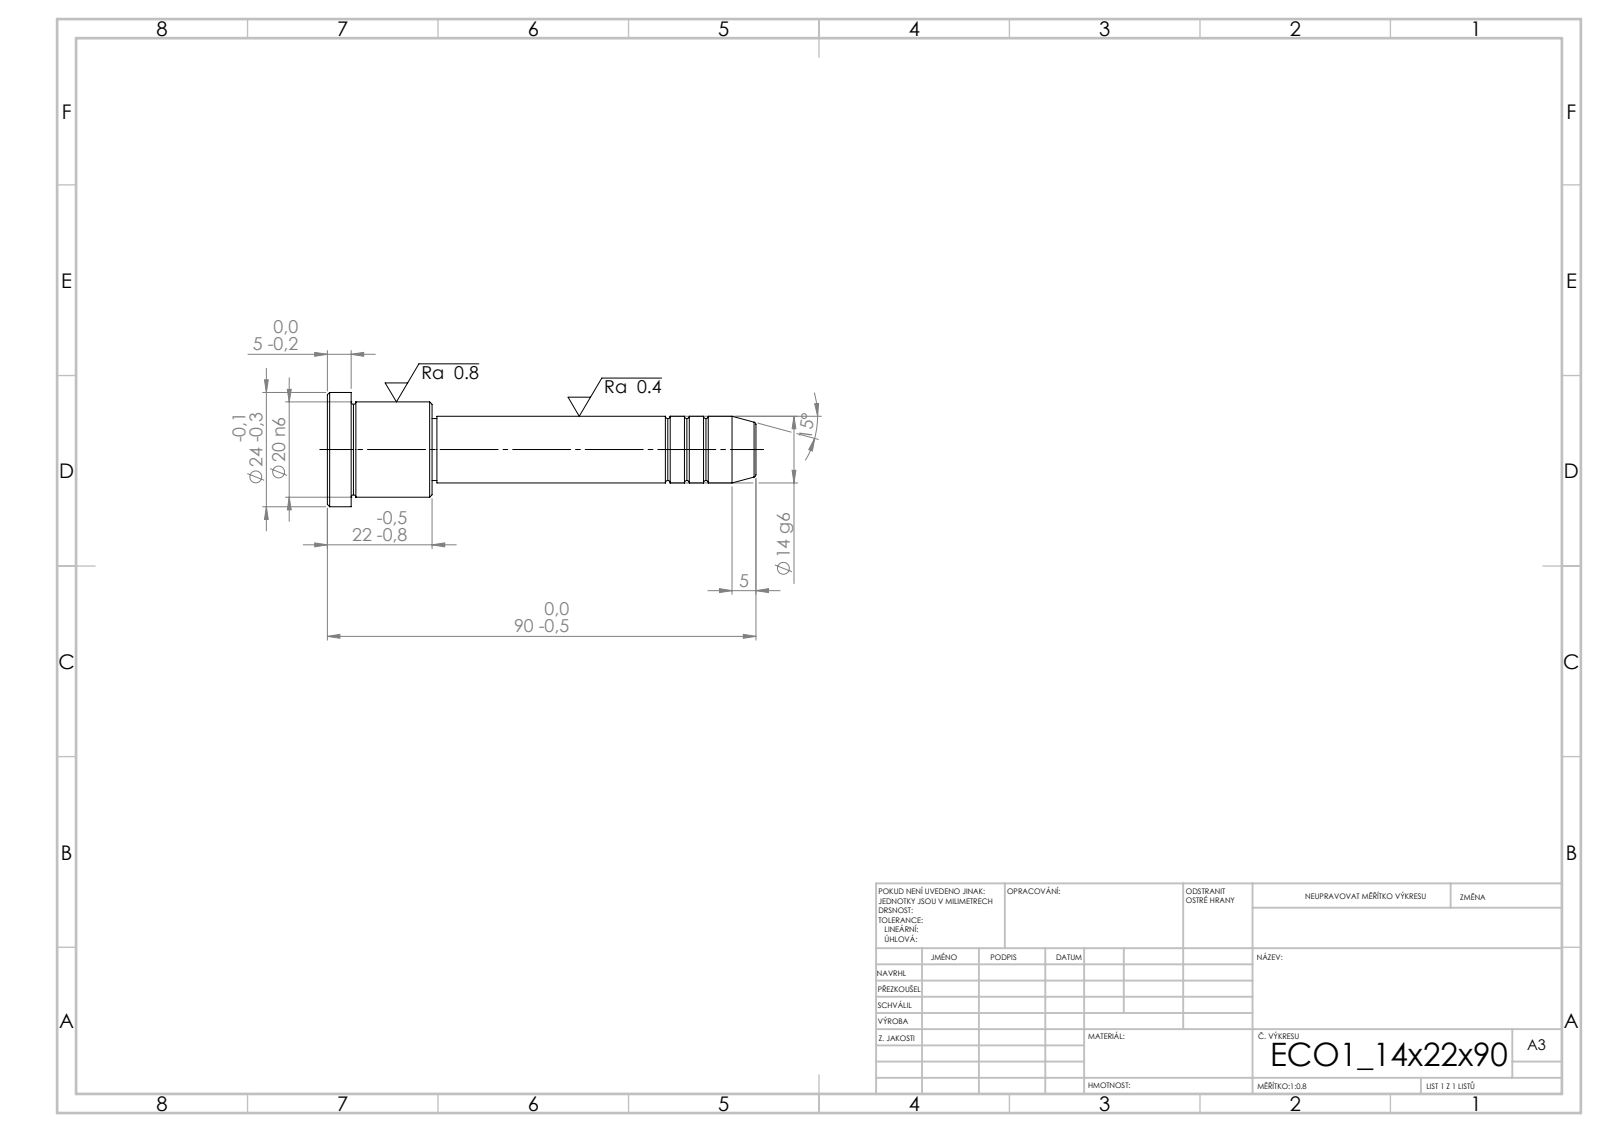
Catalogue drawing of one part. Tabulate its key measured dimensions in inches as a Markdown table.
| quantity | value |
| --- | --- |
| STEP written by | SolidWorks 2019 (CONFIG_CONTROL_DESIGN) |
| units | inches |
| bodies | 1 solid, 43 faces (5 planar, 14 cylindrical, 24 other) |
| overall size | 3.543 × 0.945 × 0.945 |
| volume | 1.087 in³ |
| surface area | 8.317 in² |
| round bosses / shafts (diameter × count) | 0.945 × 1, 0.787 × 1, 0.551 × 1, 0.512 × 1 |
| main face-to-face distances | 0.866, 0.669, 0.197, 2.677, 3.346, 3.543, 2.638, 0.039, 0.709, 0.906 |
